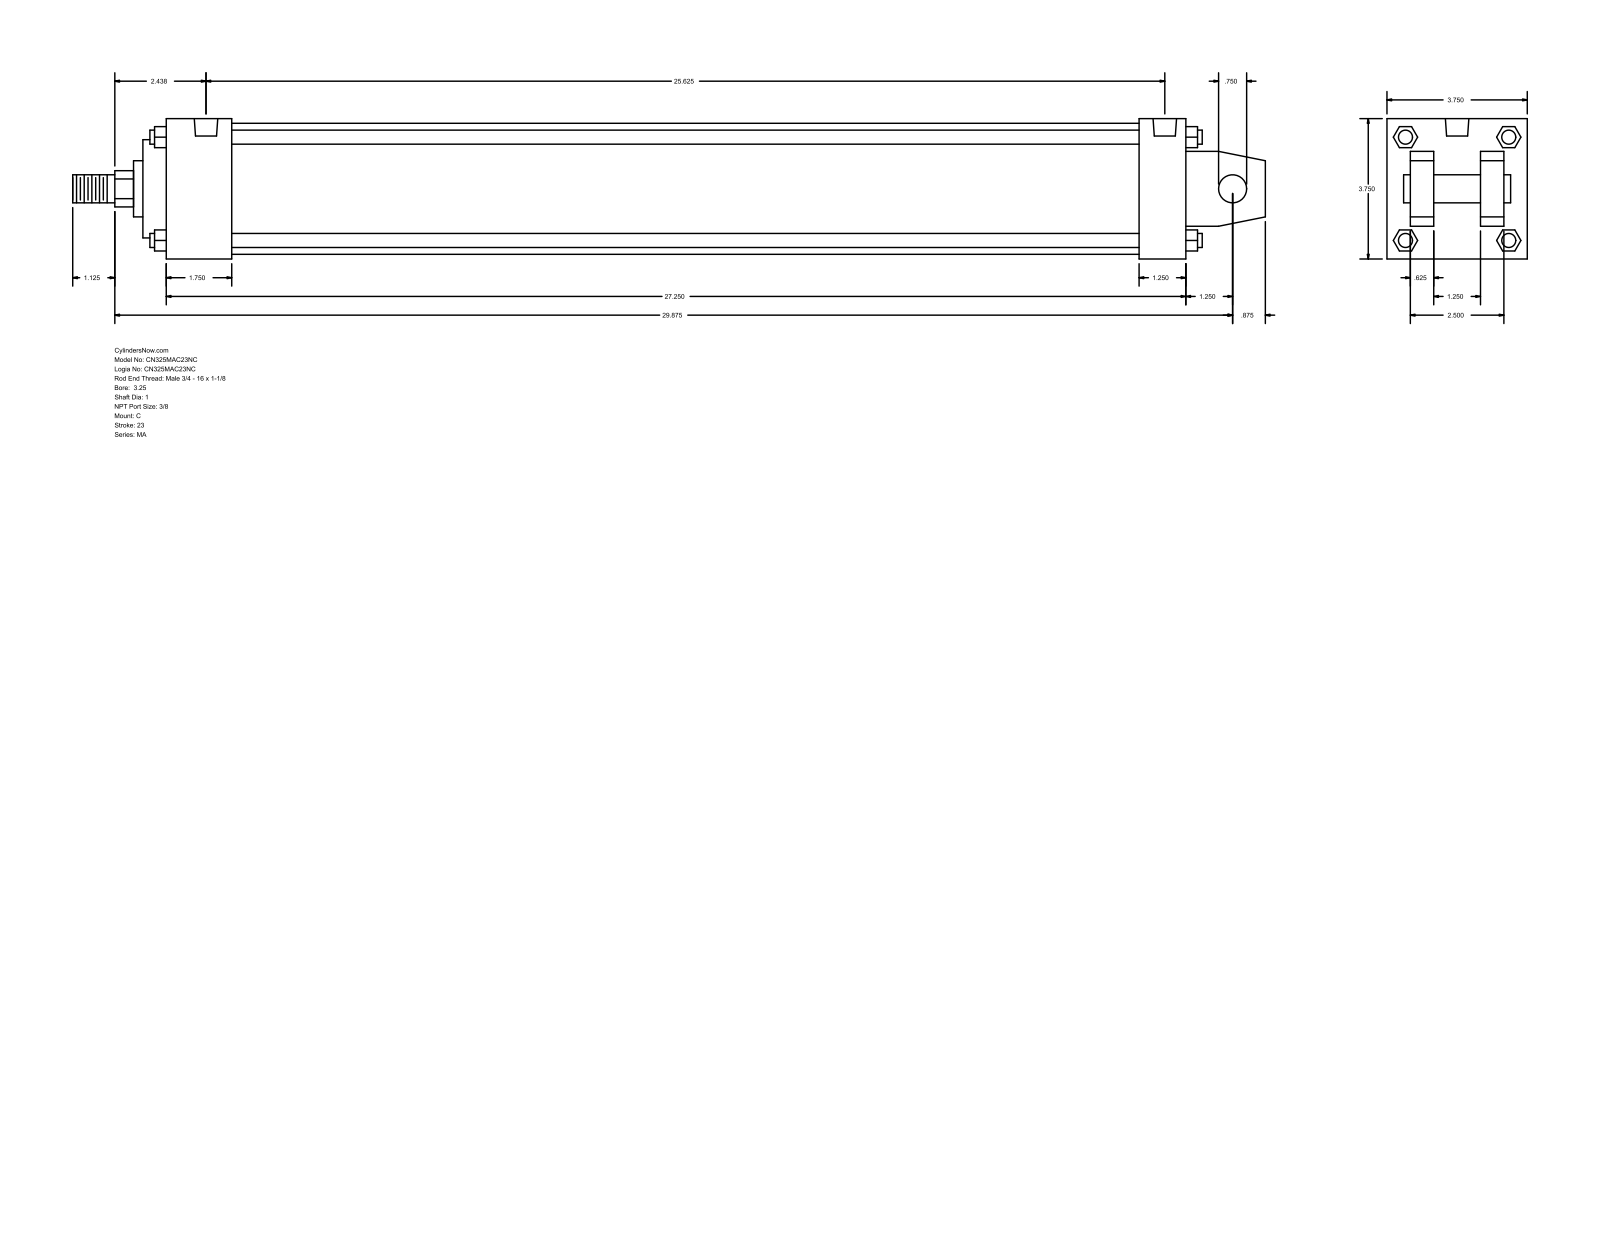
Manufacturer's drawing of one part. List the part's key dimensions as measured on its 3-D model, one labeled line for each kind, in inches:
Part name (STEP PRODUCT): MA_C__0325_1
STEP written by: GSSL Pune (CONFIG_CONTROL_DESIGN)
Units: inches
Bodies: 0 solids, 141 faces (109 planar, 32 cylindrical, 0 other)
Overall size (bounding box): 31.875 × 3.75 × 3.75
Round holes (diameter × count): ⌀0.437 ×4, ⌀0.627 ×2
Round bosses / shafts (diameter × count): ⌀0.375 ×4, ⌀0.75 ×2, ⌀3.5 ×1, ⌀2.625 ×1, ⌀1.5 ×1, ⌀1 ×1
Partial cylindrical surfaces — rounded edges, fillets, slot ends (radius × count): R0.484 ×1
Main face-to-face distances: 3.75, 0.625, 2.5, 27.25, 1.25, 3.125, 1.875, 26, 1.25, 1.75
Hole centre spacings: 25.25, 0.187, 0.188, 25.437, 25.438, 25.625
